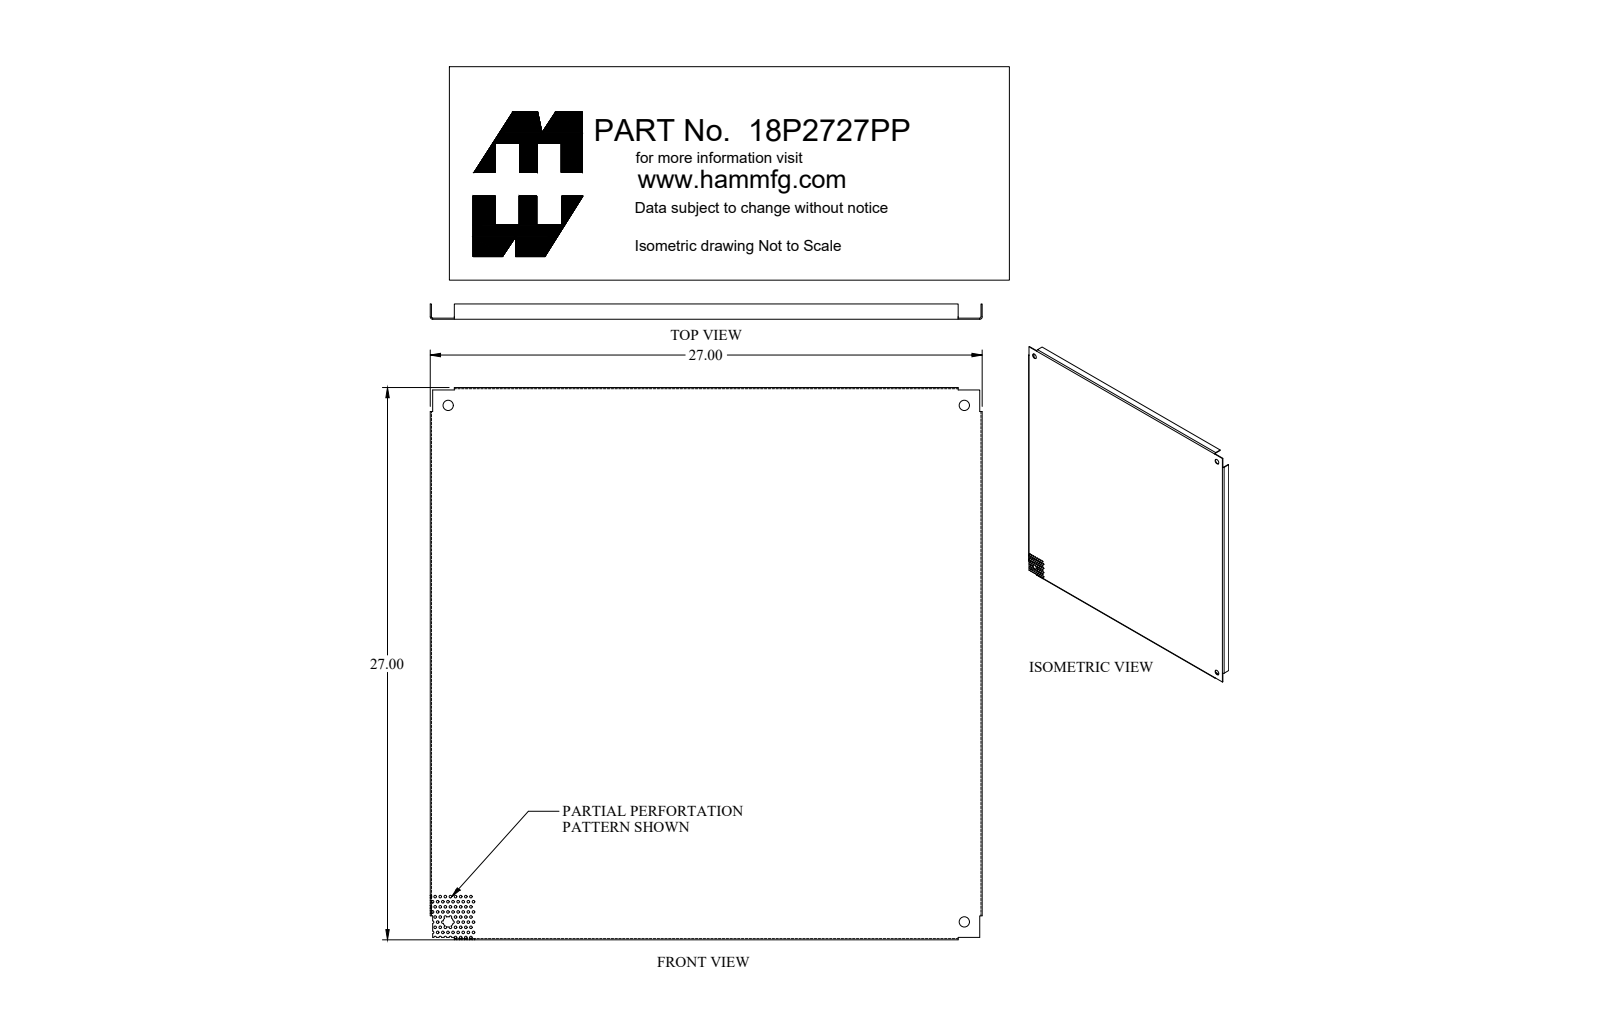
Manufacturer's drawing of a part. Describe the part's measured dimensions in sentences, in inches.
The part is named "18P2727PP_Default". Its 3-D file was written by "SolidWorks 2018 (CONFIG_CONTROL_DESIGN)". It is 1 solid with 254 faces: 43 planar, 203 cylindrical and 8 other. Overall it measures 27 by 27 by 0.75 inches. Its volume is 45.15 cubic inches and its surface area 1 593 square inches. Round holes: 74 of diameter 0.125, 3 of diameter 0.5. Partial cylindrical surfaces (rounded edges, fillets, slot ends): 17 of radius 0.063, 8 of radius 0.062, 4 of radius 0.029, 4 of radius 0.086, 1 of radius 0.25. The main face-to-face distances are 0.057, 26.943, 27, 26.886, 0.75, 0.693, 0.102, 26.898, 0.045, 26.841. The hole center spacings are 0.28, 0.5, 0.25, 0.559, 0.451, 0.76, 0.707, 0.75.
